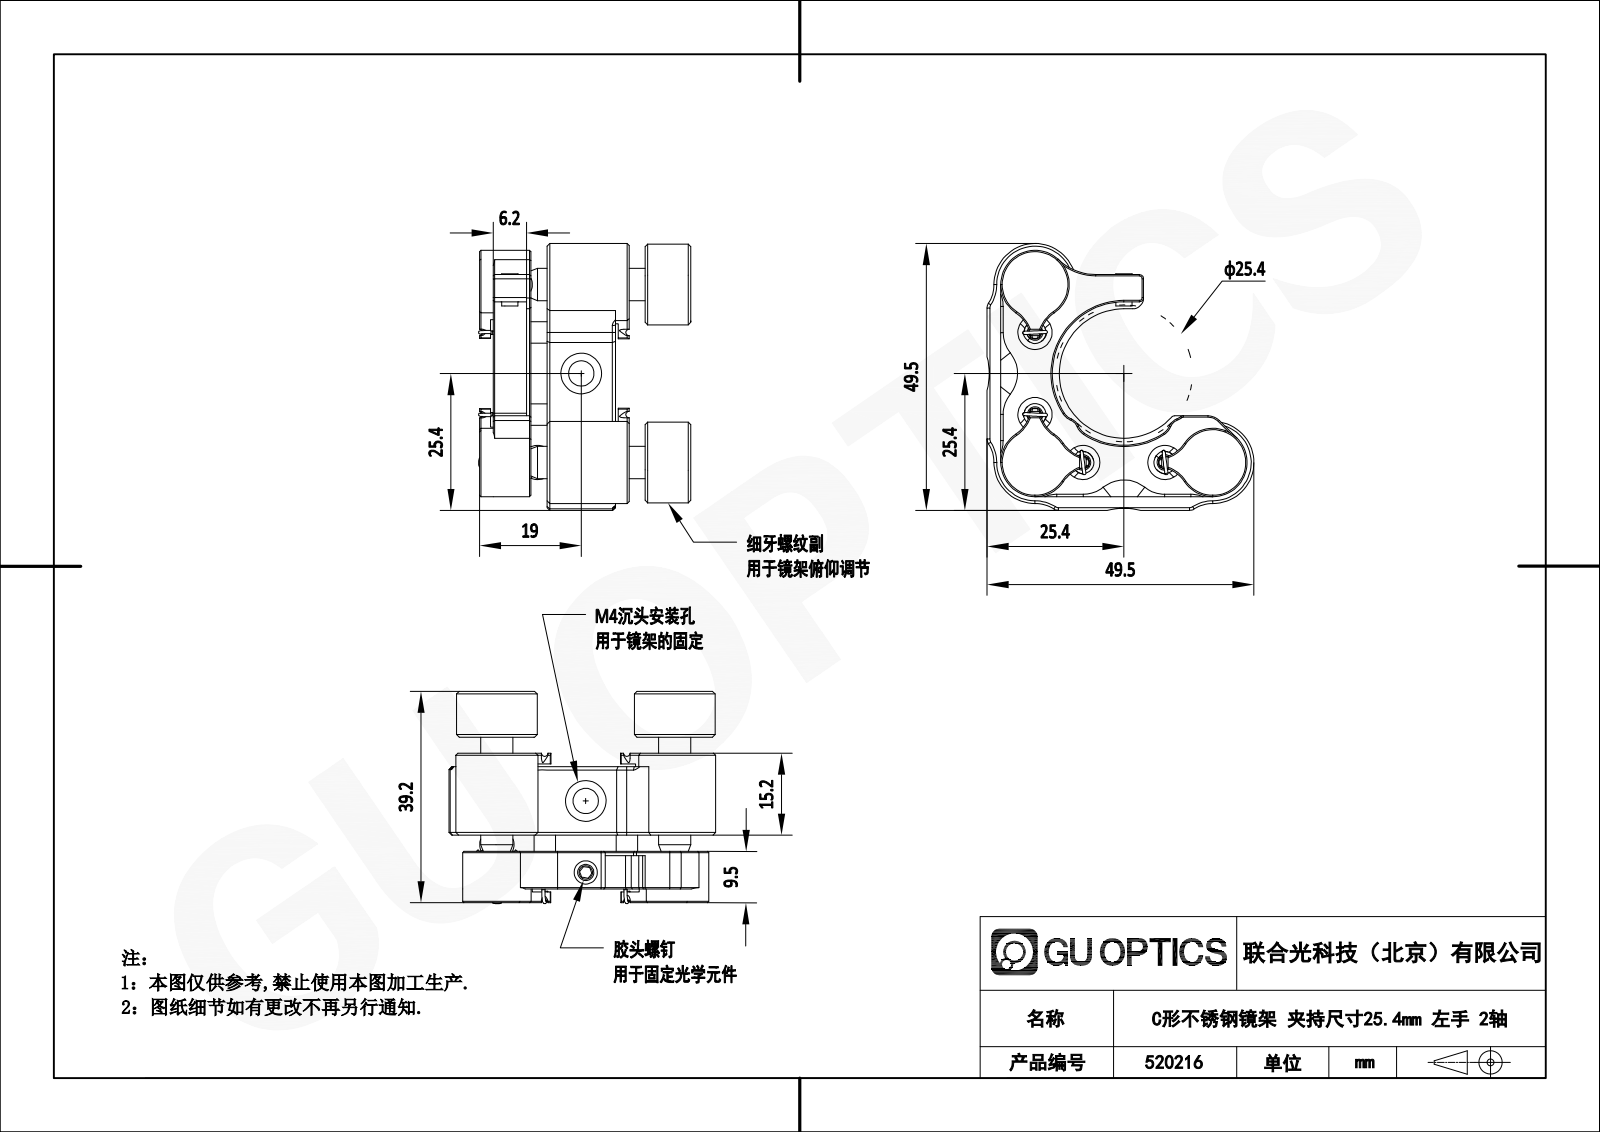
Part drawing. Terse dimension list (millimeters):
name: 30.8.8-14，M4尼龙头顶丝，A_30.8.9-LNJ4*5; DXG，平面螺纹旋钮_3.2.10.19-DXG-M0625-15-8.5S; TL-耳5x0.8_2; 36.1，440c不锈钢滚珠_36.1.6_GZ-B4 (+5 more)
written by: SolidWorks 2021 (CONFIG_CONTROL_DESIGN)
unit: mm
bodies: 26 solids, 664 faces (209 planar, 163 cylindrical, 292 other)
size: 49.53 × 49.53 × 40.51
volume: 23 171 mm³; area: 15 362 mm²
holes: 6× ⌀6.35, 4× ⌀2.4, 2× ⌀2.01, 2× ⌀3.99, 2× ⌀4, 2× ⌀4.7, 2× ⌀6, 2× ⌀7, 2× ⌀7.54, 1× ⌀3.3
bosses: 9× ⌀4, 2× ⌀15.24, 2× ⌀15, 2× ⌀12.7, 1× ⌀3
rounds: 22× R6.48, 5× R3, 4× R0.8, 4× R1, 4× R1.93, 4× R3.17, 2× R1.59, 2× R1.59
face distances: 2.54, 25.52, 3.3, 18.54, 6.98, 15.24, 10.28, 22.98, 16, 12.7
hole spacings: 5, 8.89, 15.24, 24.13, 25.72, 34.2, 40.9, 12.57
